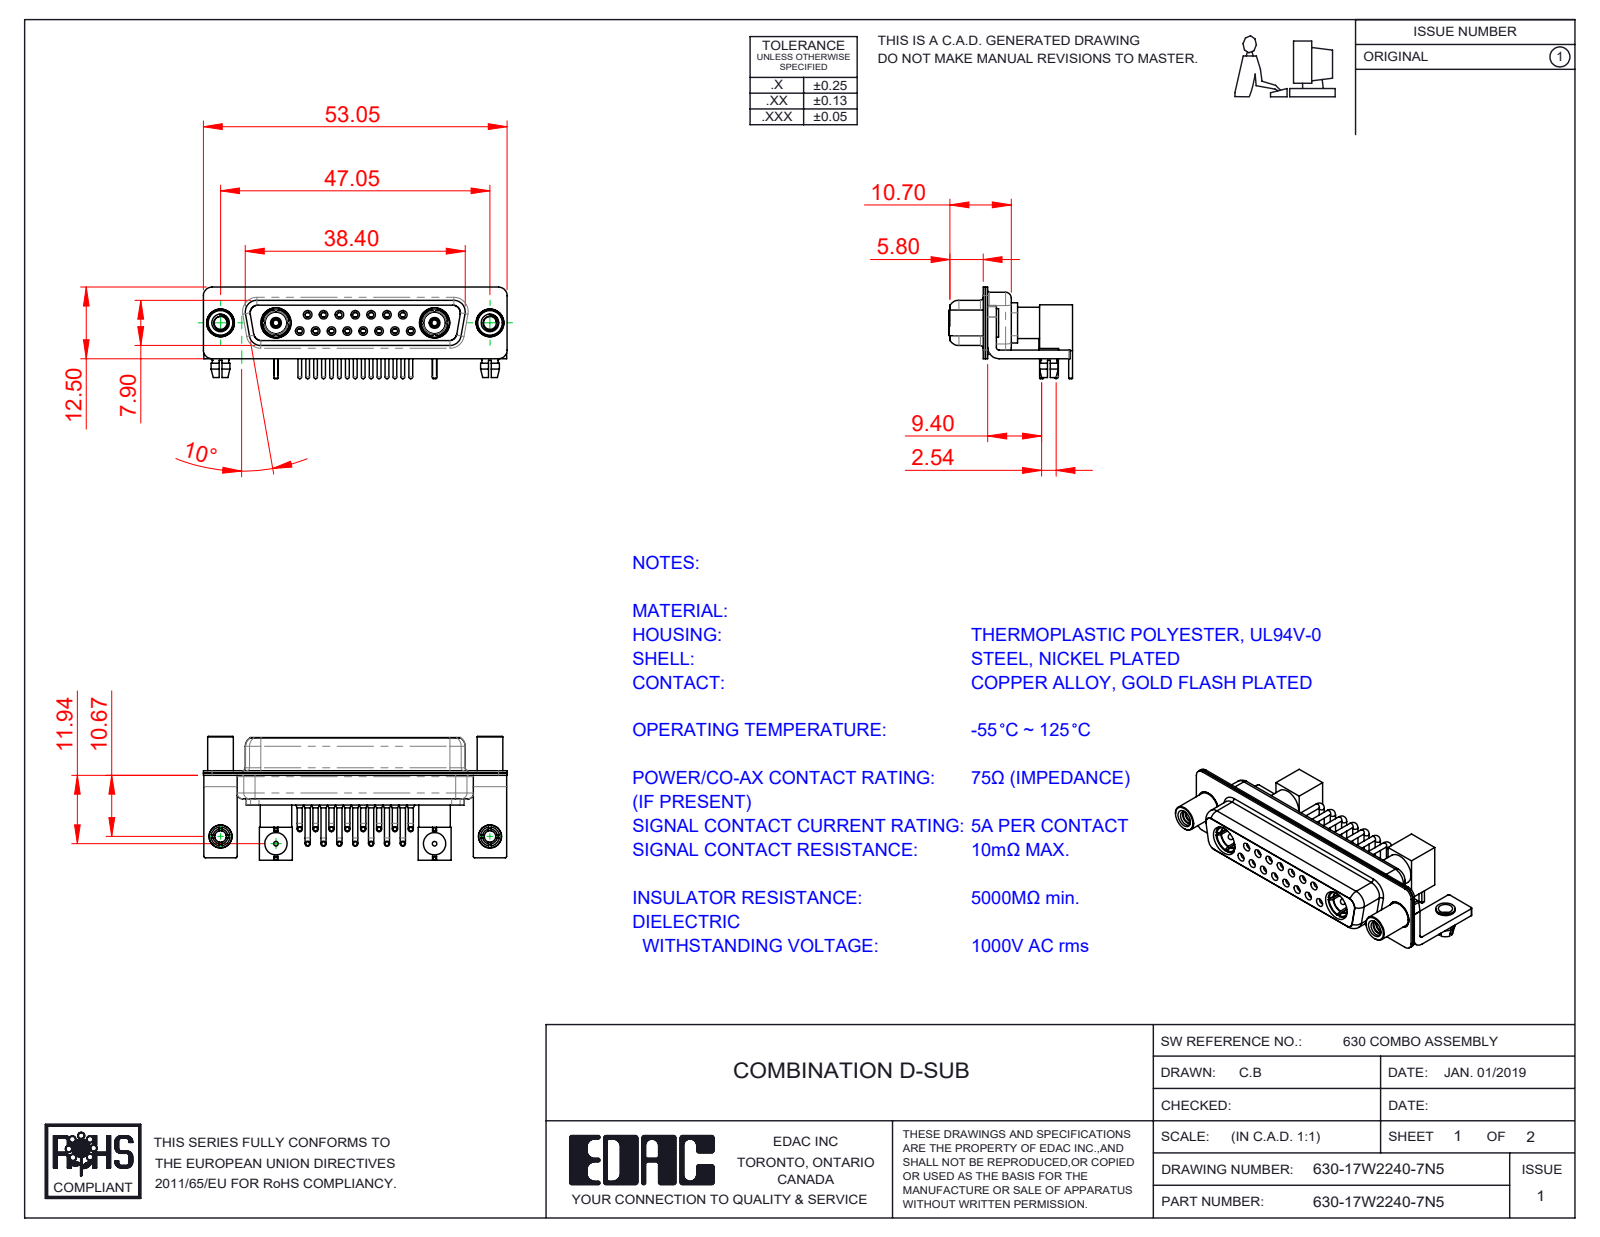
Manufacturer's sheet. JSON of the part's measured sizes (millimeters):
{"part_name": "Pin_RA; 630Combo Board Lock; 630Combo Contact Row 2; 630Combo Contact Row 1 (+8 more)", "step_written_by": "SolidWorks 2020 (CONFIG_CONTROL_DESIGN)", "units": "millimeters", "bodies": {"solids": 36, "faces": 1590, "planar": 496, "cylindrical": 704, "other": 390}, "overall_size": [53.05, 21.61, 16], "volume_mm3": 4789, "surface_area_mm2": 11545, "round_holes": [[1.1, 17], [1.5, 17], [2, 17], [0.9, 15], [1.6, 8], [1.7, 7], [4.85, 4], [0.8, 2], [2.26, 2], [2.5, 2], [2.83, 2], [3.1, 2]], "round_bosses_or_shafts": [[0.9, 15], [0.65, 15], [1.6, 7], [5, 4], [4, 4], [2.9, 4], [0.8, 3], [5.5, 2]], "partial_cylinders_radius": [[0.25, 16], [1.5, 16], [2, 13], [1.35, 8], [1.6, 8], [0.5, 5], [0.6, 4], [0.65, 4]], "face_to_face_distances": [0.4, 1.4, 0.45, 1.8, 8.45, 0.8, 8.9, 6.2, 7.05, 1.35], "hole_center_spacings": [3.16, 2.77, 5.54, 8.31, 5.04, 7.49, 11.08, 5.03]}
